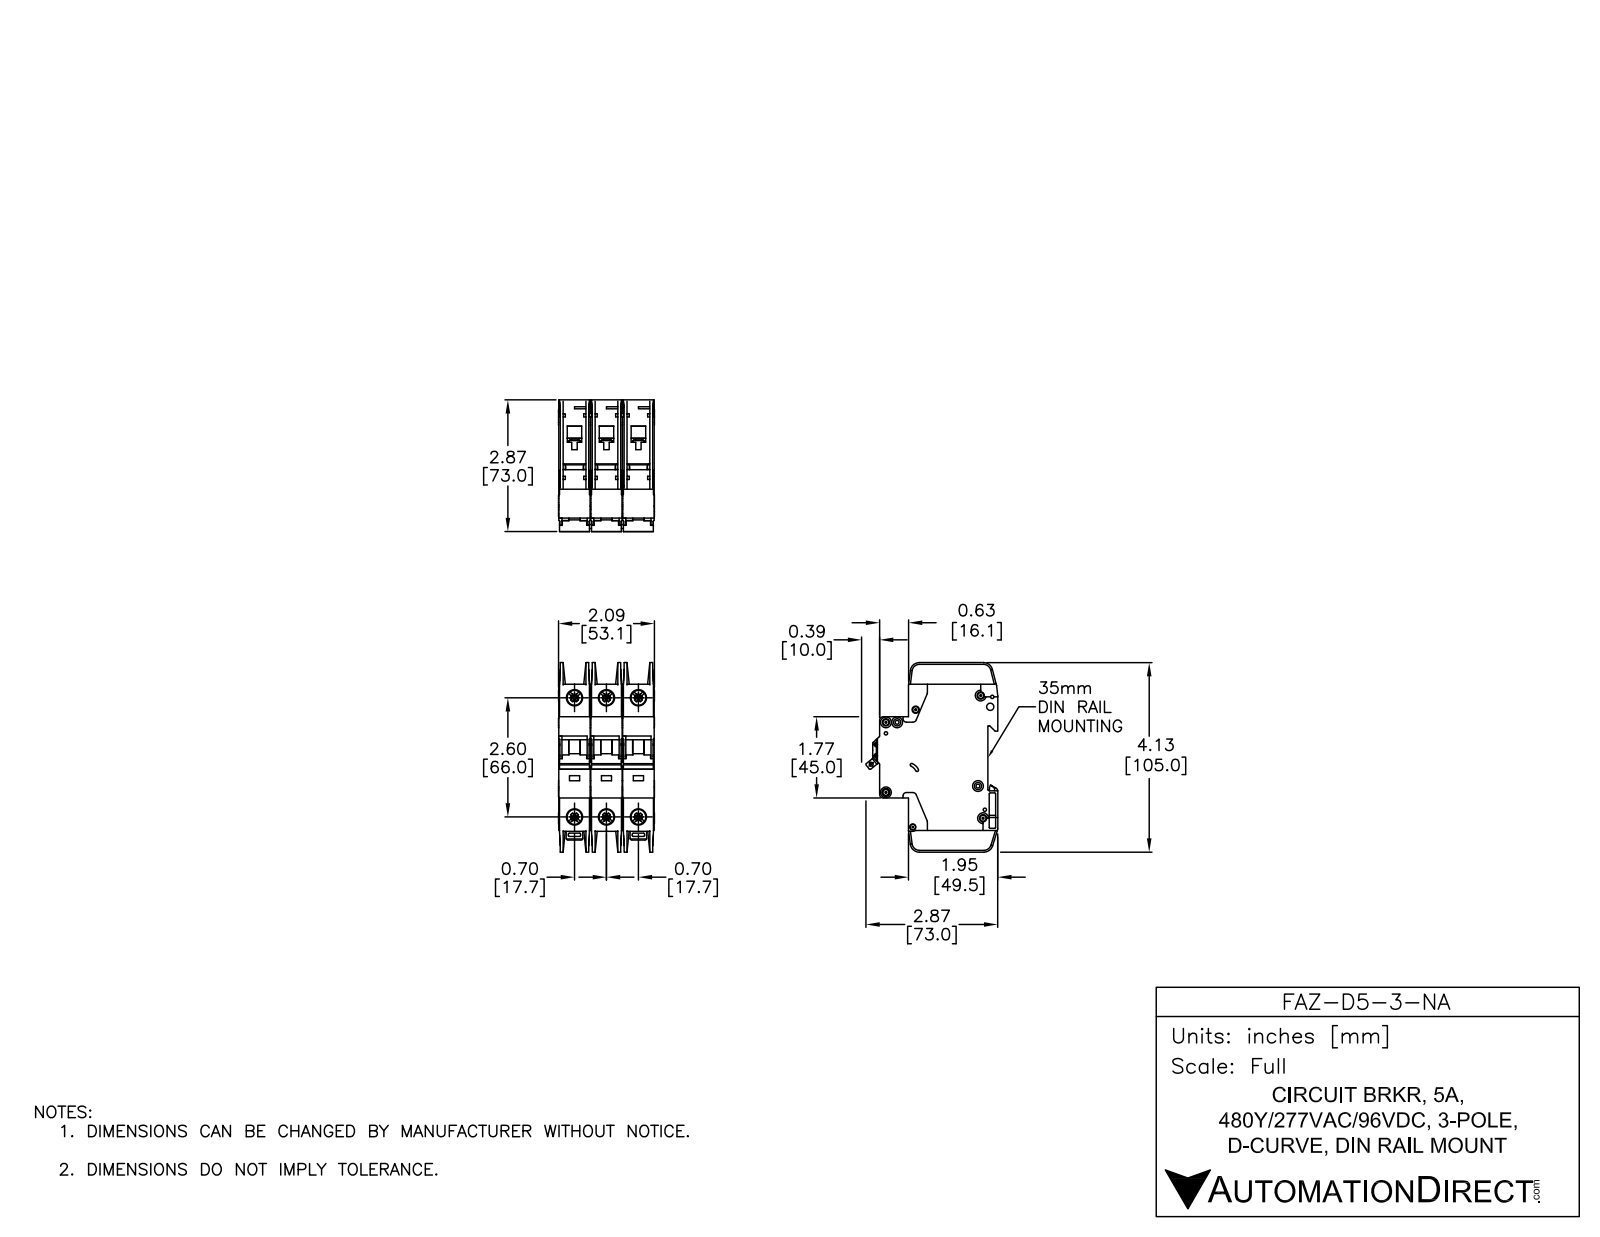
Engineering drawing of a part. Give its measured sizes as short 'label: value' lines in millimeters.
name: FAZ-D5-3-NA
written by: SolidWorks 2014 (AUTOMOTIVE_DESIGN)
unit: mm
bodies: 9 solids, 2352 faces (1227 planar, 789 cylindrical, 336 other)
size: 105 × 73.04 × 53.1
volume: 233 085 mm³; area: 74 219 mm²
holes: 7× ⌀3.6, 6× ⌀7.15, 6× ⌀8.2, 2× ⌀1.09, 2× ⌀1.5, 2× ⌀4, 1× ⌀1.9, 1× ⌀2.15, 1× ⌀2.2, 1× ⌀2.55, 1× ⌀3.3, 1× ⌀3.4
bosses: 7× ⌀6, 3× ⌀2.5
rounds: 65× R0.25, 30× R0.5, 26× R1, 14× R2, 5× R1.8, 5× R5, 4× R4, 2× R0.2
face distances: 17.7, 35.4, 17.5, 35.2, 0.7, 15.05, 2.45, 1.75, 15.75, 13.3
hole spacings: 17.7, 68.33, 66, 6.2, 35.4, 74.89, 5.19, 6.1
